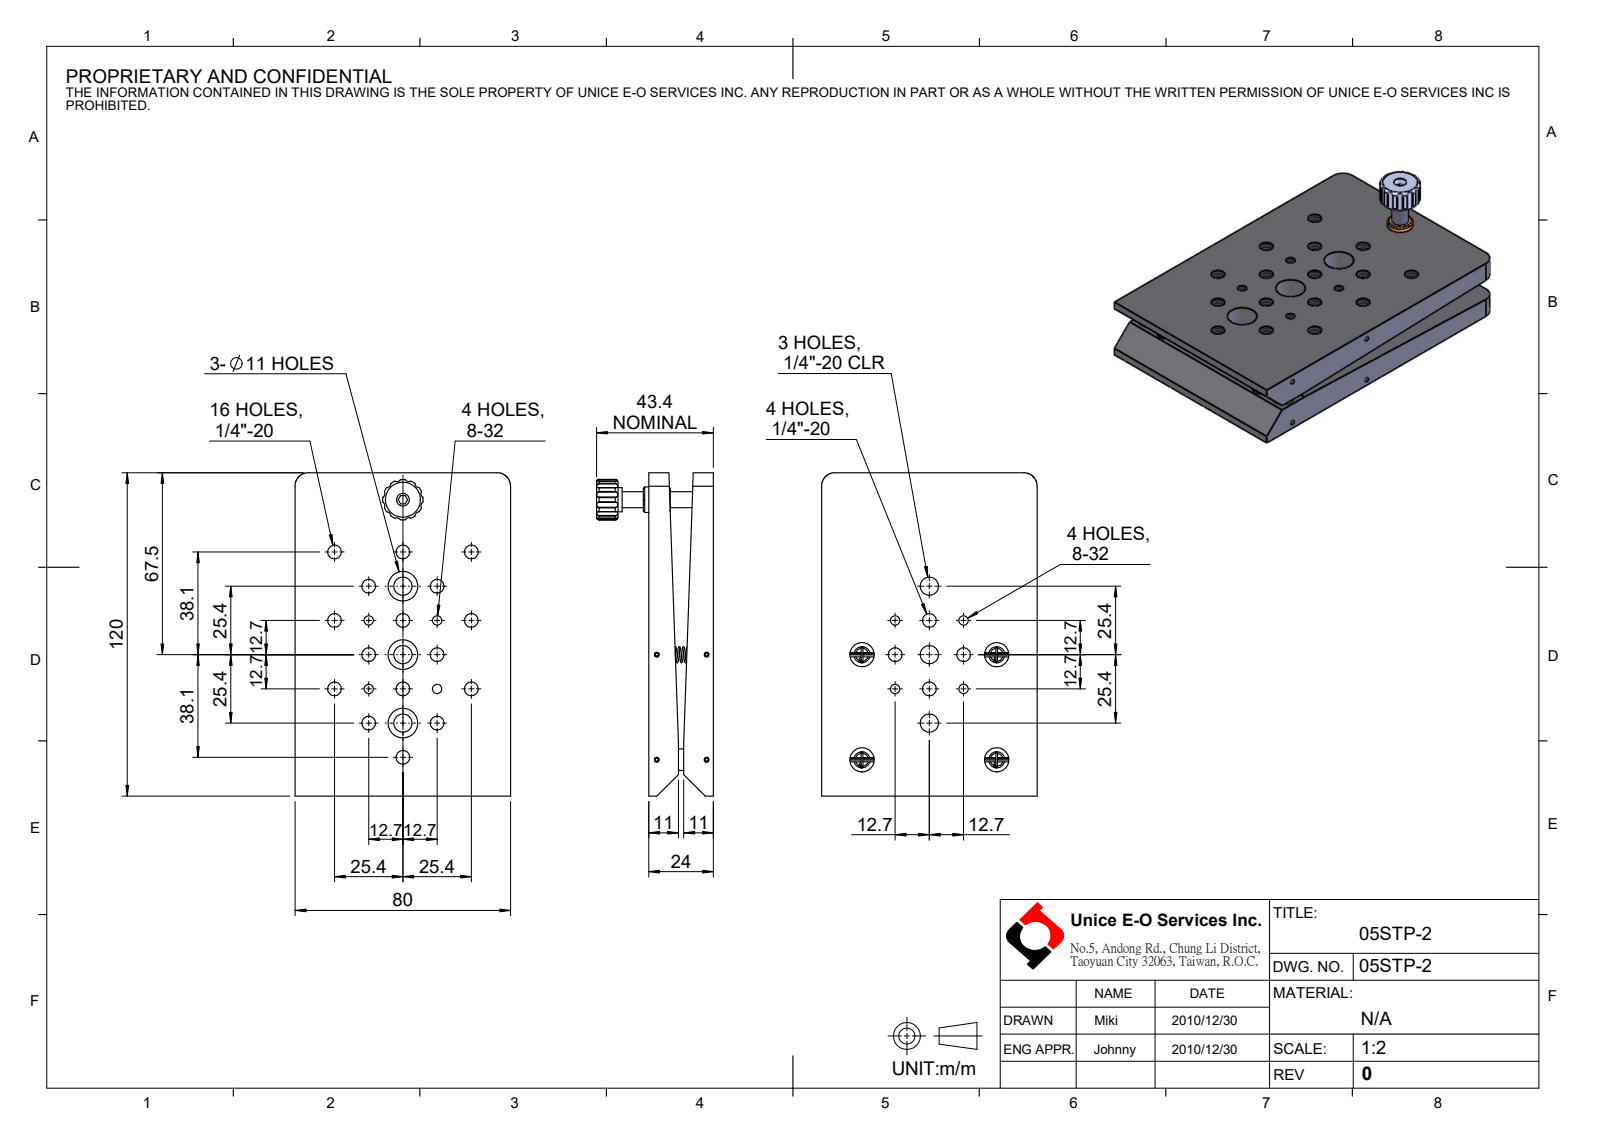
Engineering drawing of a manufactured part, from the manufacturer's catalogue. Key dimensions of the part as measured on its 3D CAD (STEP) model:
Part name (STEP PRODUCT): 05STP-2
STEP written by: SolidWorks 2016 (CONFIG_CONTROL_DESIGN)
Units: millimetres
Bodies: 22 solids, 386 faces (97 planar, 227 cylindrical, 62 other)
Overall size (bounding box): 120 × 80 × 43.4
Volume: 165 405 mm³ · Surface area: 57 173 mm²
Round holes (diameter × count): ⌀5.11 ×16, ⌀1.2 ×4, ⌀1.8 ×4, ⌀3.45 ×4, ⌀9 ×4, ⌀6.76 ×3, ⌀11 ×3, ⌀11.51 ×3, ⌀3.3 ×1, ⌀4 ×1, ⌀4.7 ×1, ⌀5 ×1
Round bosses / shafts (diameter × count): ⌀1.6 ×4, ⌀0.6 ×4, ⌀9.5 ×1, ⌀9 ×1, ⌀4 ×1
Partial cylindrical surfaces — rounded edges, fillets, slot ends (radius × count): R0.3 ×24, R1.5 ×12, R5 ×2, R7.5 ×1
Main face-to-face distances: 24, 80, 13, 11, 2, 120, 10, 23, 12, 1
Hole centre spacings: 28.4, 17.96, 12.7, 40.16, 25.4, 35.92, 45.79, 38.1
